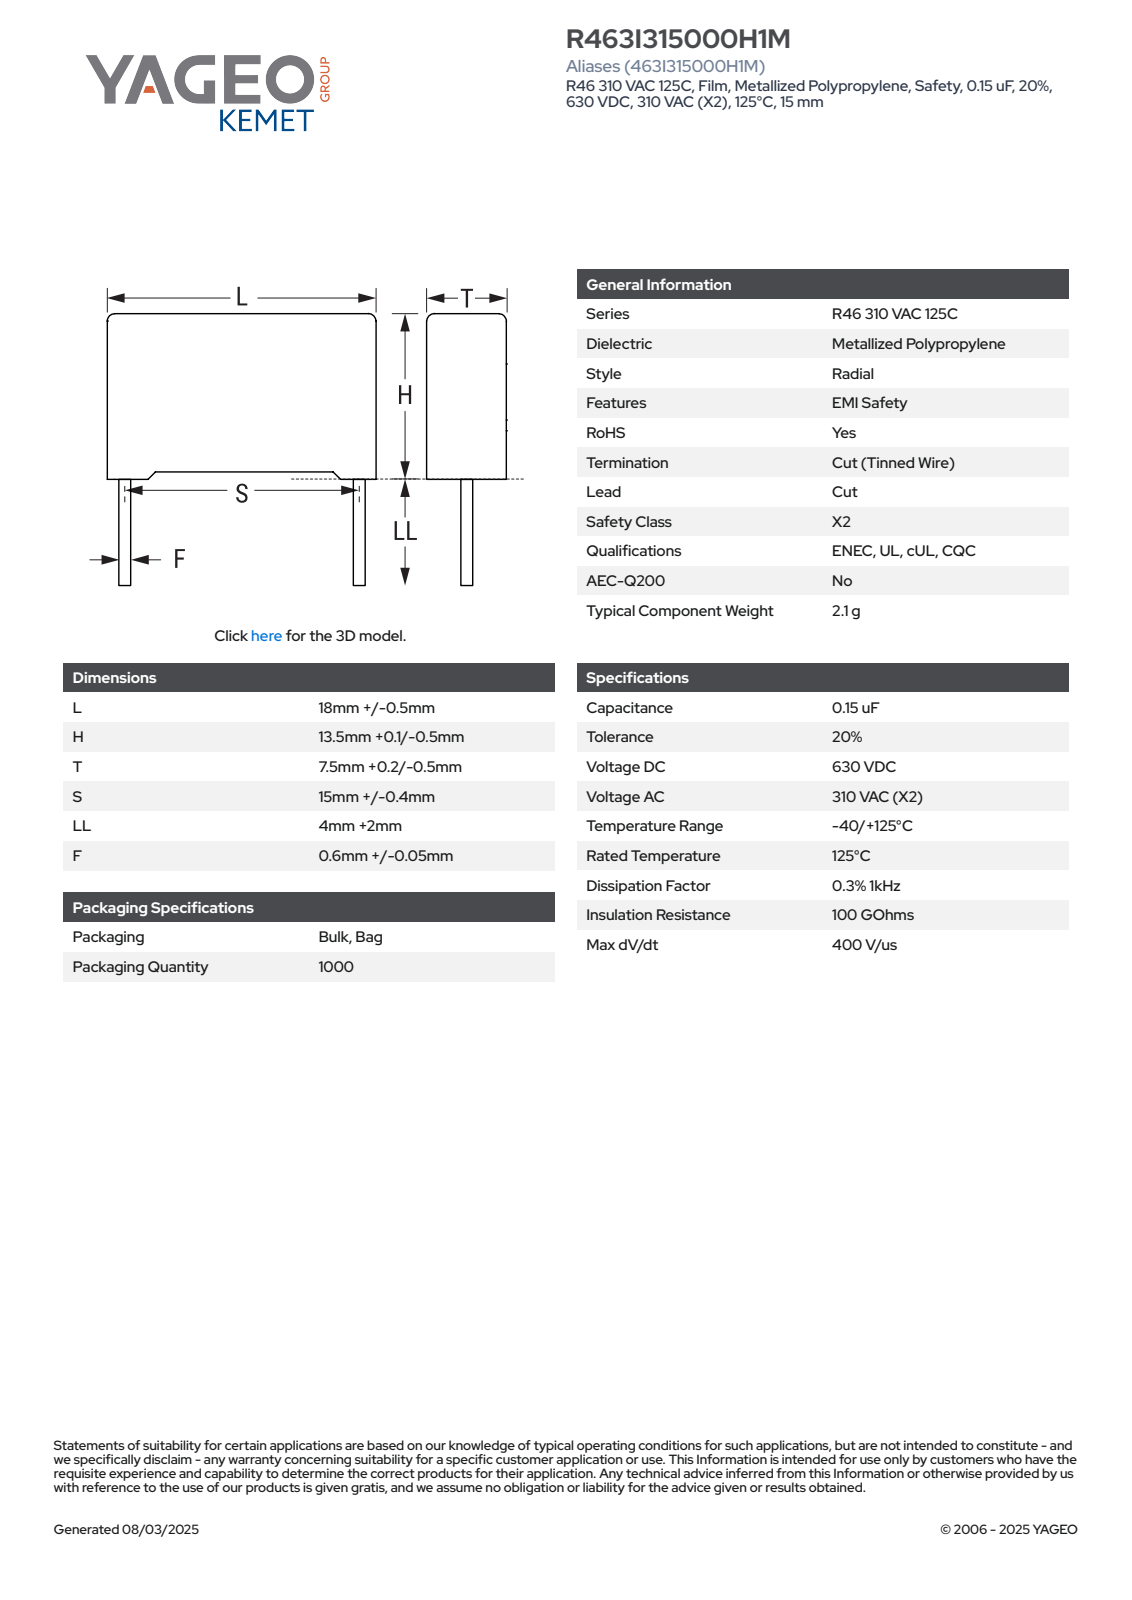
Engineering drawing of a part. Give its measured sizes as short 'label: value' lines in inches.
name: CFR_RB2_18X12X6_L18.5H13.6T7.7S15LL6F0.65
written by: SolidWorks 2021 (AUTOMOTIVE_DESIGN)
unit: in
bodies: 4 solids, 85 faces (77 planar, 8 cylindrical, 0 other)
size: 0.772 × 0.709 × 0.304
volume: 0.11 in³; area: 1.598 in²
bosses: 2× ⌀0.026
rounds: 4× R0.02
face distances: 0.303, 0.506, 0.709, 0.024, 0.03, 0.535, 0.28, 0.019, 0.517, 0.685
